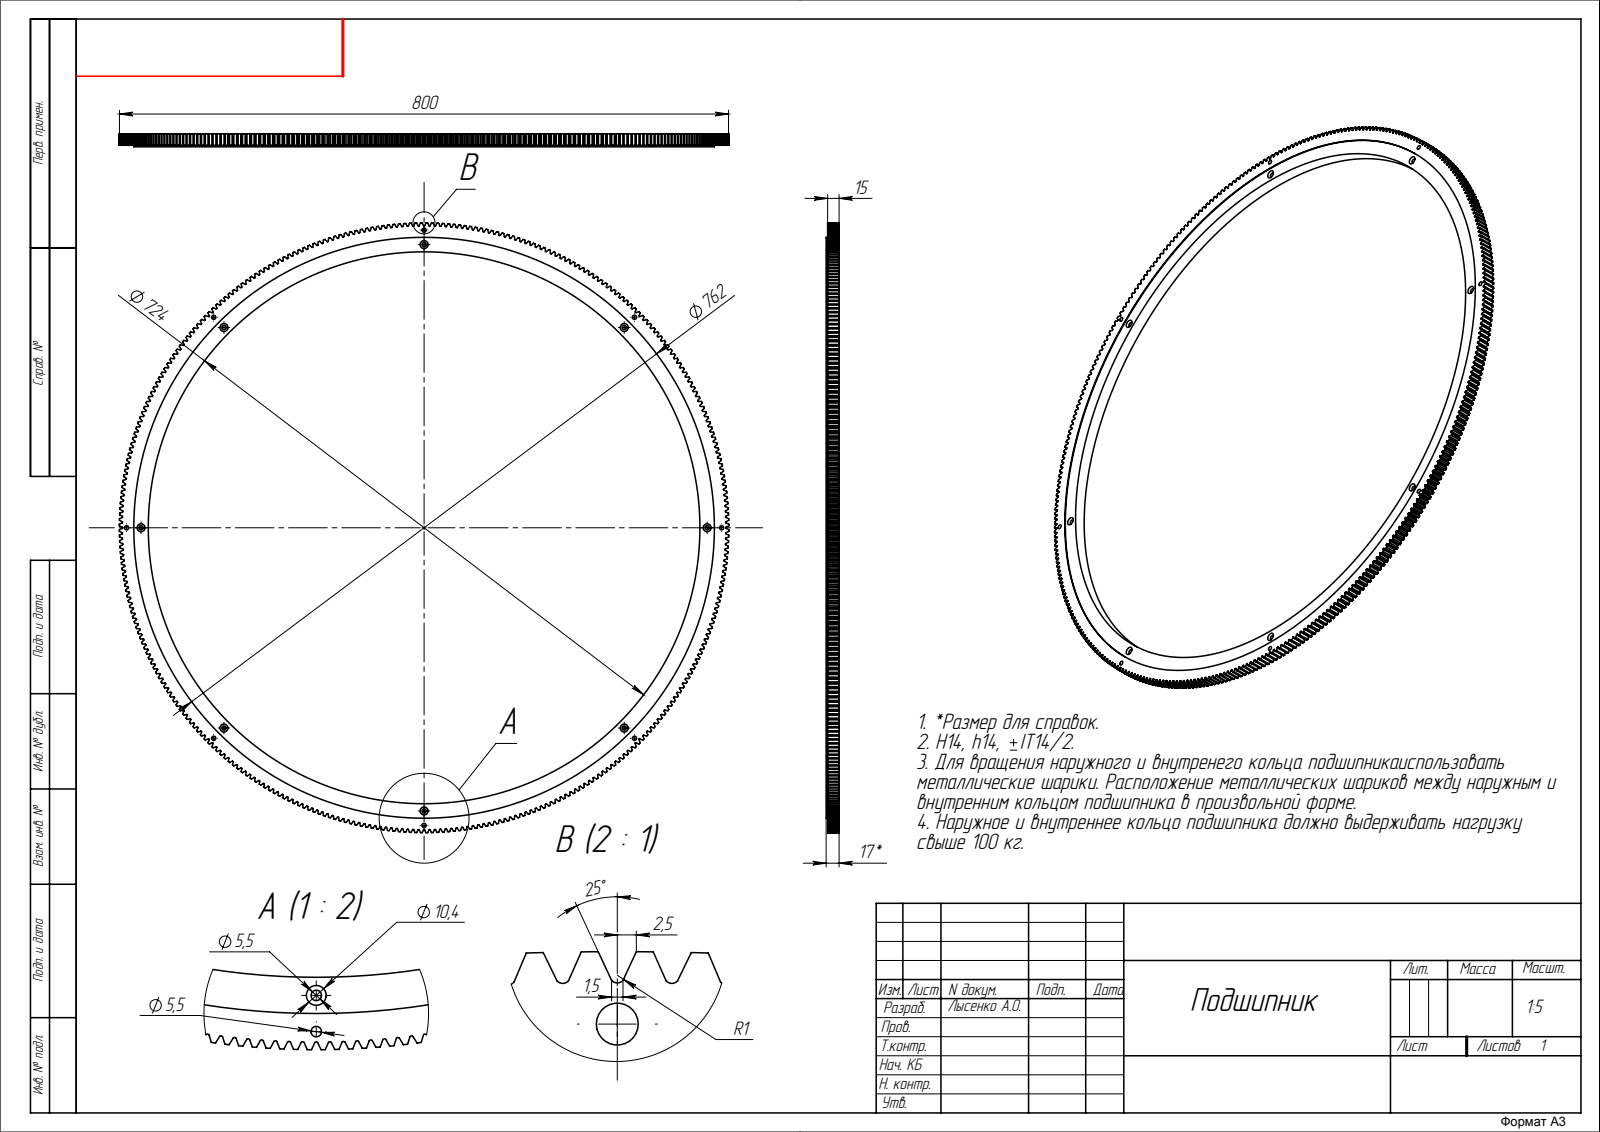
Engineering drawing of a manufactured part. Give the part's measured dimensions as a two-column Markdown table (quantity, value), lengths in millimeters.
| quantity | value |
| --- | --- |
| part name | Внутреннее кольцо подшипника; Подшипник; Наружное кольцо подшипника с зубьями |
| STEP written by | SolidWorks 2016 (CONFIG_CONTROL_DESIGN) |
| units | millimeters |
| bodies | 2 solids, 1559 faces (700 planar, 827 cylindrical, 32 other) |
| overall size | 799.98 × 799.98 × 17 |
| volume | 1 336 000 mm³ |
| surface area | 350 723 mm² |
| round holes (diameter × count) | 5.5 × 16, 724 × 1, 762 × 1 |
| partial cylindrical surfaces (radius × count) | 1 × 348, 400 × 1 |
| main face-to-face distances | 16, 17, 1, 2, 14, 15, 333.62, 333.52, 333.6, 333.56 |
| hole center spacings | 284.33, 292.13, 292.14, 298.88, 371.5, 525.38, 538.98, 538.99 |
